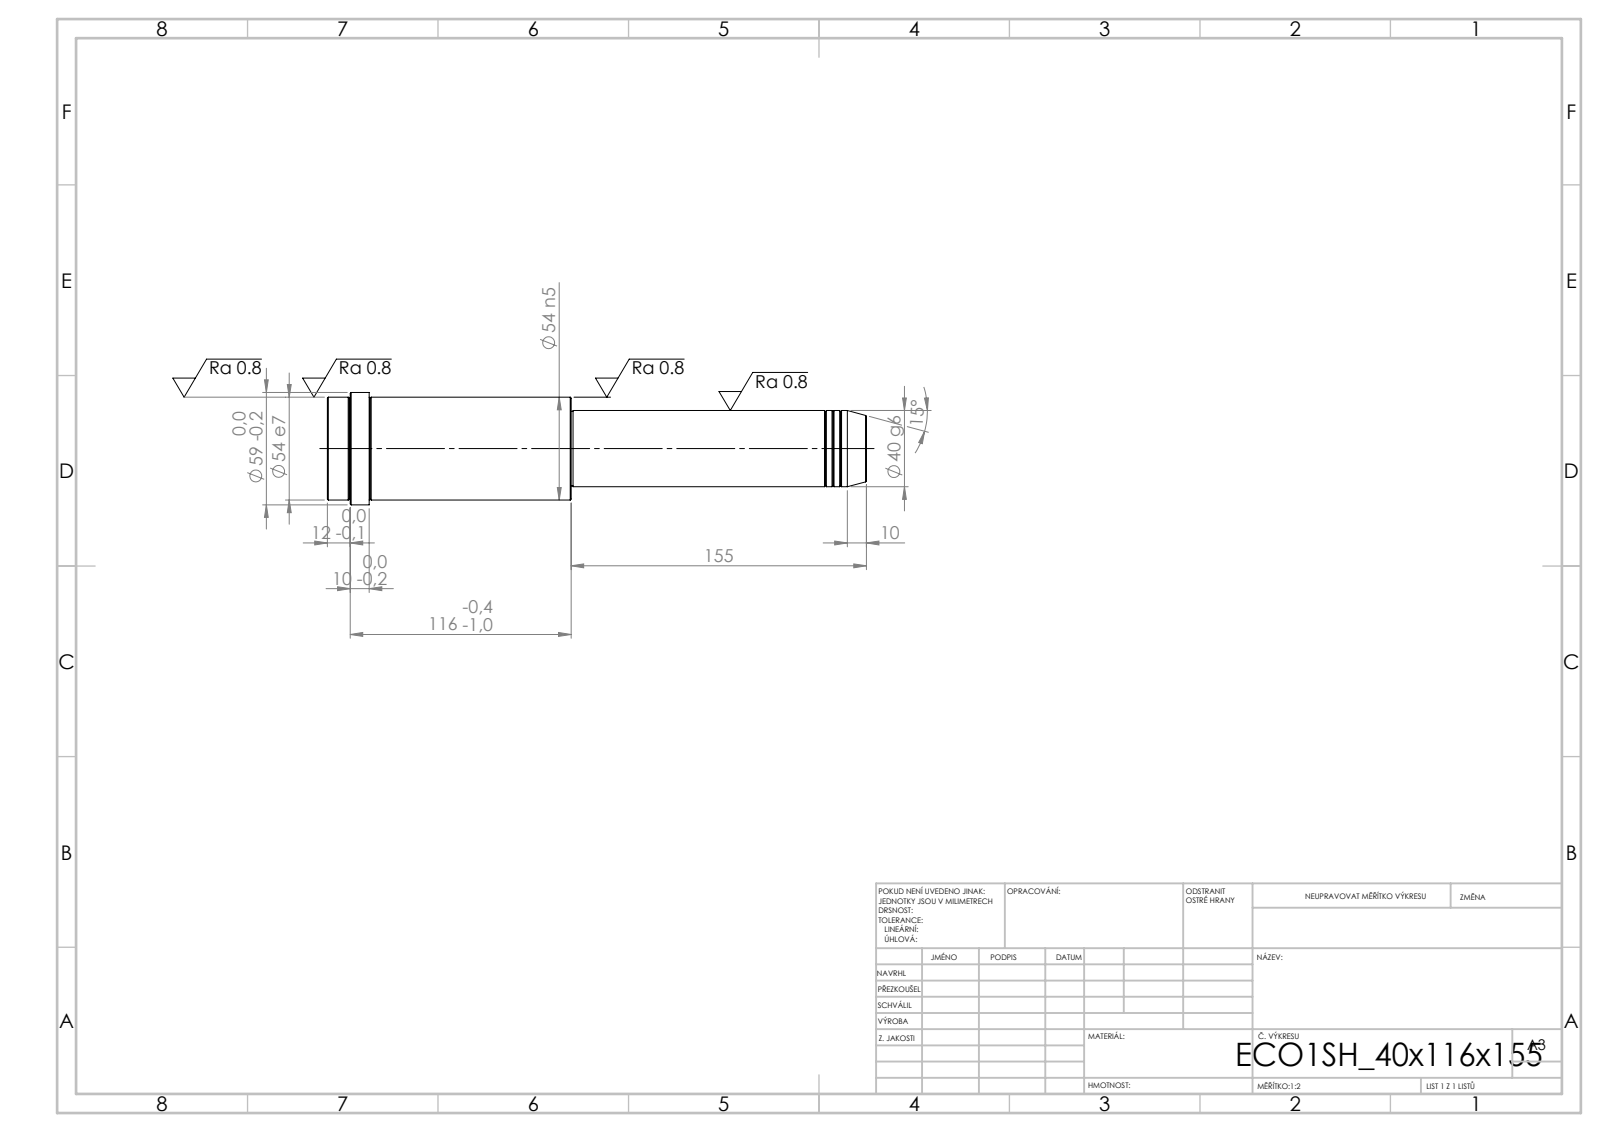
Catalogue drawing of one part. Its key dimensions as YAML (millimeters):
step_written_by: "SolidWorks 2019 (CONFIG_CONTROL_DESIGN)"
units: millimeters
bodies: {solids: 1, faces: 52, planar: 6, cylindrical: 16, other: 30}
overall_size: [283, 59, 59]
volume: 490347
surface_area: 46808
round_bosses_or_shafts:
  - {diameter: 59, count: 1}
  - {diameter: 54, count: 1}
  - {diameter: 40, count: 1}
  - {diameter: 39, count: 1}
face_to_face_distances: [128, 155, 283, 261, 106, 22, 271, 116, 10, 12]
